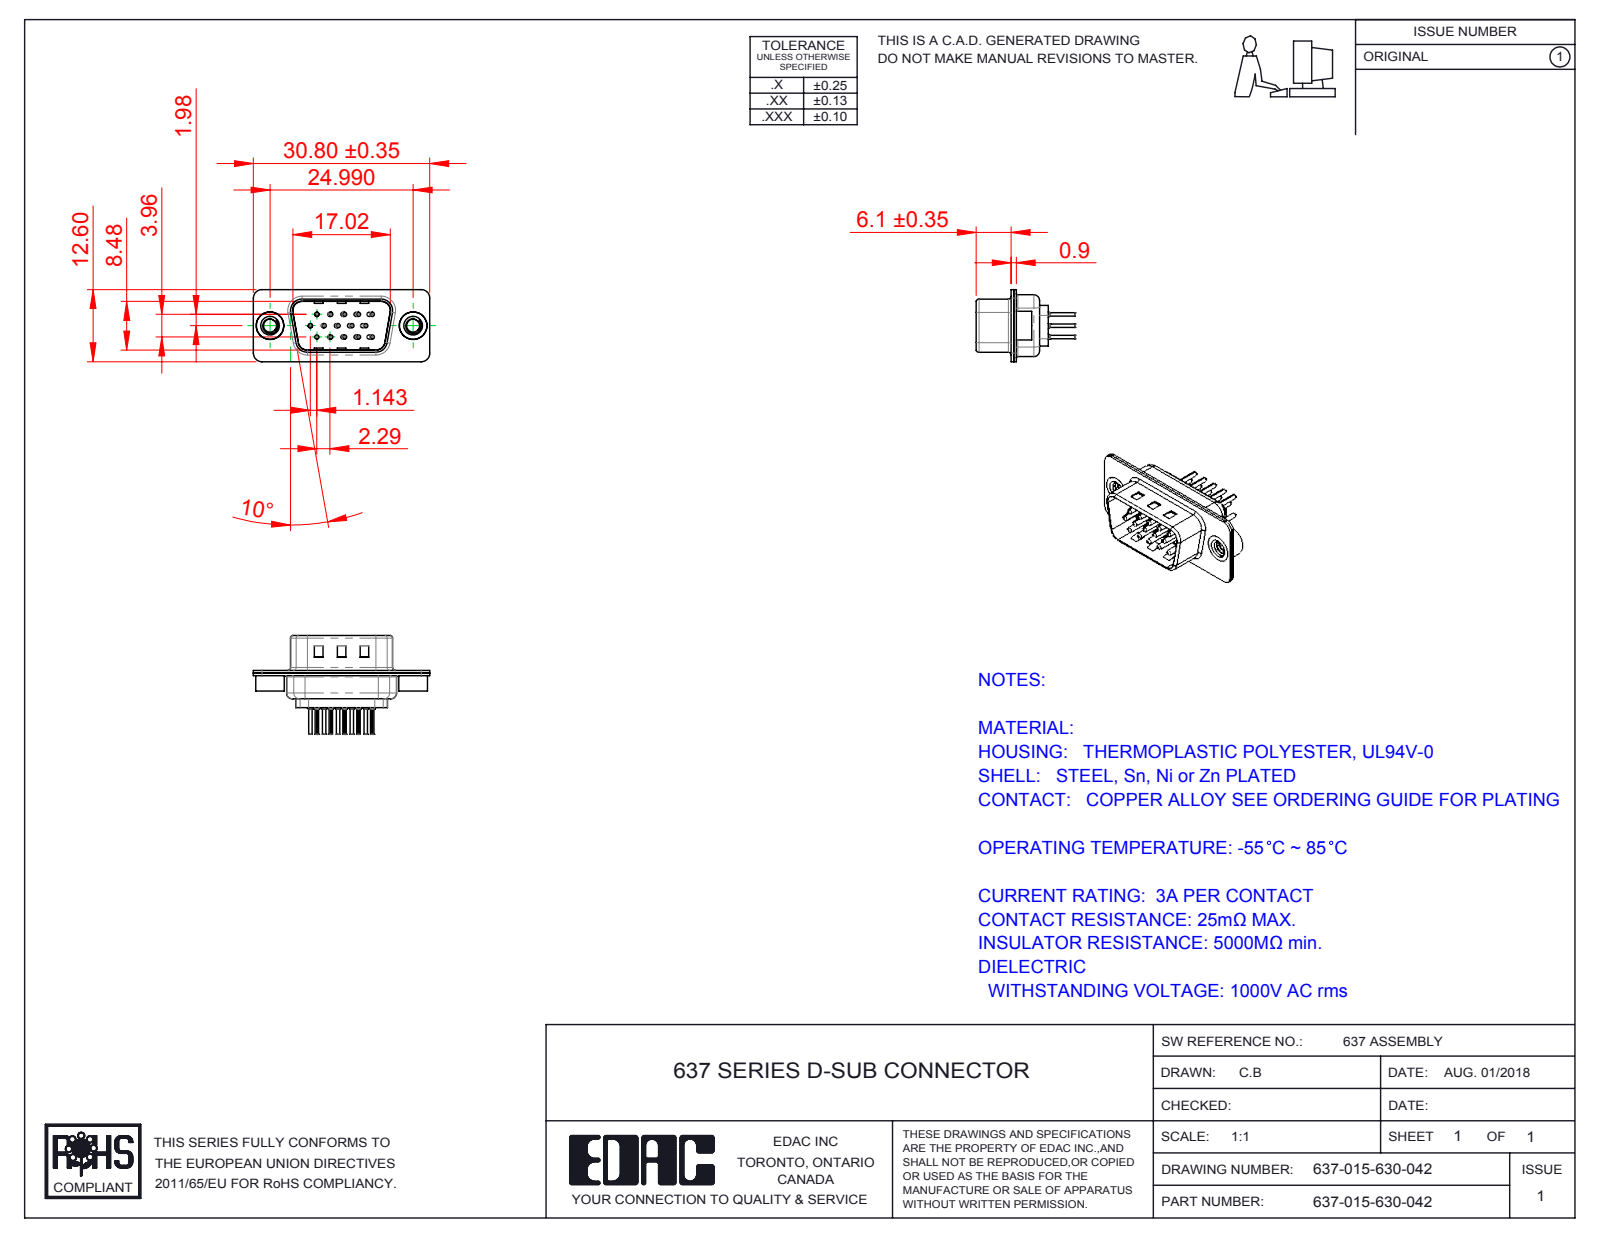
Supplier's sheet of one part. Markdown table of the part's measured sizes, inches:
| quantity | value |
| --- | --- |
| part name | 637 Housing_15 Contacts; 637 Contact Row 1_30; 637-015-630-042; 637 Contact Row 2_30 (+4 more) |
| STEP written by | SolidWorks 2016 (CONFIG_CONTROL_DESIGN) |
| units | inches |
| bodies | 20 solids, 1804 faces (467 planar, 684 cylindrical, 653 other) |
| overall size | 1.213 × 0.679 × 0.496 |
| volume | 0.08 in³ |
| surface area | 7.203 in² |
| round holes (diameter × count) | 0.063 × 27, 0.008 × 15, 0.014 × 15, 0.043 × 15, 0.03 × 12, 0.079 × 12, 0.089 × 2, 0.157 × 2, 0.189 × 2 |
| round bosses / shafts (diameter × count) | 0.079 × 15, 0.059 × 15, 0.03 × 15, 0.024 × 15, 0.197 × 2, 0.193 × 2 |
| partial cylindrical surfaces (radius × count) | 0.004 × 30, 0.059 × 16, 0.079 × 12, 0.02 × 8, 0.01 × 4, 0.022 × 4, 0.028 × 4, 0.037 × 4 |
| main face-to-face distances | 0.018, 0.035, 0.016, 0.334, 0.028, 0.35, 0.012, 0.179, 0.041, 0.046 |
| hole center spacings | 0.156, 0.09, 0.09, 0.18, 0.095, 0.238, 0.191, 0.093 |
